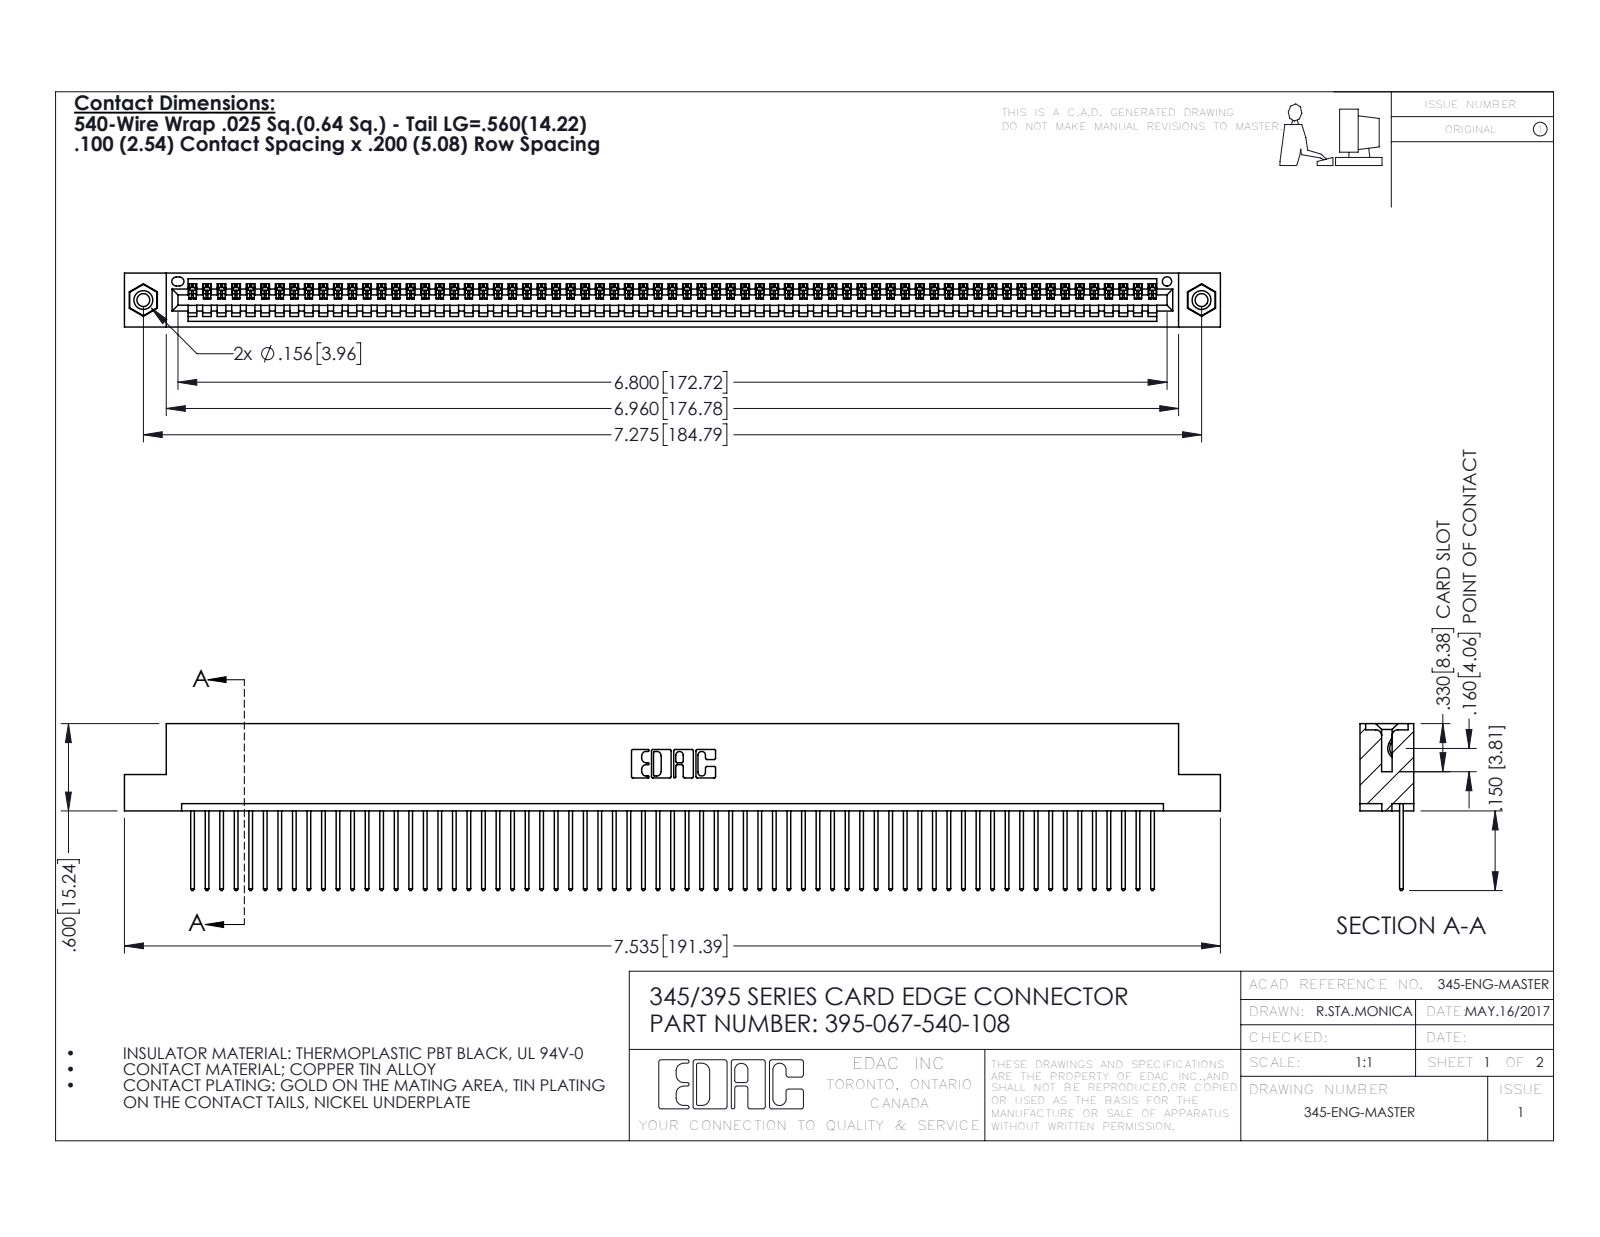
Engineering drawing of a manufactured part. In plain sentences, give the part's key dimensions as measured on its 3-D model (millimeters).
The part is named "345-250-001_345-250-003-102; 395-067-540-108; 345-292-001_345-293-140; 345 Part_Flush Mounting Lugs - 0.156 Dia-TI". Its 3-D file was written by "SolidWorks 2016 (CONFIG_CONTROL_DESIGN)". It is 70 solids with 4072 faces: 2792 planar, 1264 cylindrical and 16 other. Overall it measures 191.4 by 29.1 by 9.4 millimeters. Its volume is 18 470 cubic millimeters and its surface area 25 550 square millimeters. Round holes: 2 of diameter 2.3, 2 of diameter 3.2, 2 of diameter 4, 1 of diameter 1.6. Round bosses or shafts: 2 of diameter 3.9. Partial cylindrical surfaces (rounded edges, fillets, slot ends): 134 of radius 0.2, 134 of radius 0.3, 22 of radius 0.3, 6 of radius 0.2, 6 of radius 0.8, 3 of radius 0.7, 2 of radius 0.8, 2 of radius 1. The main face-to-face distances are 1.8, 7.6, 9.4, 2.5, 6.9, 0.6, 5.1, 5.7, 3.8, 1.8. The hole center spacings are 6.9, 178.8, 184.8.
